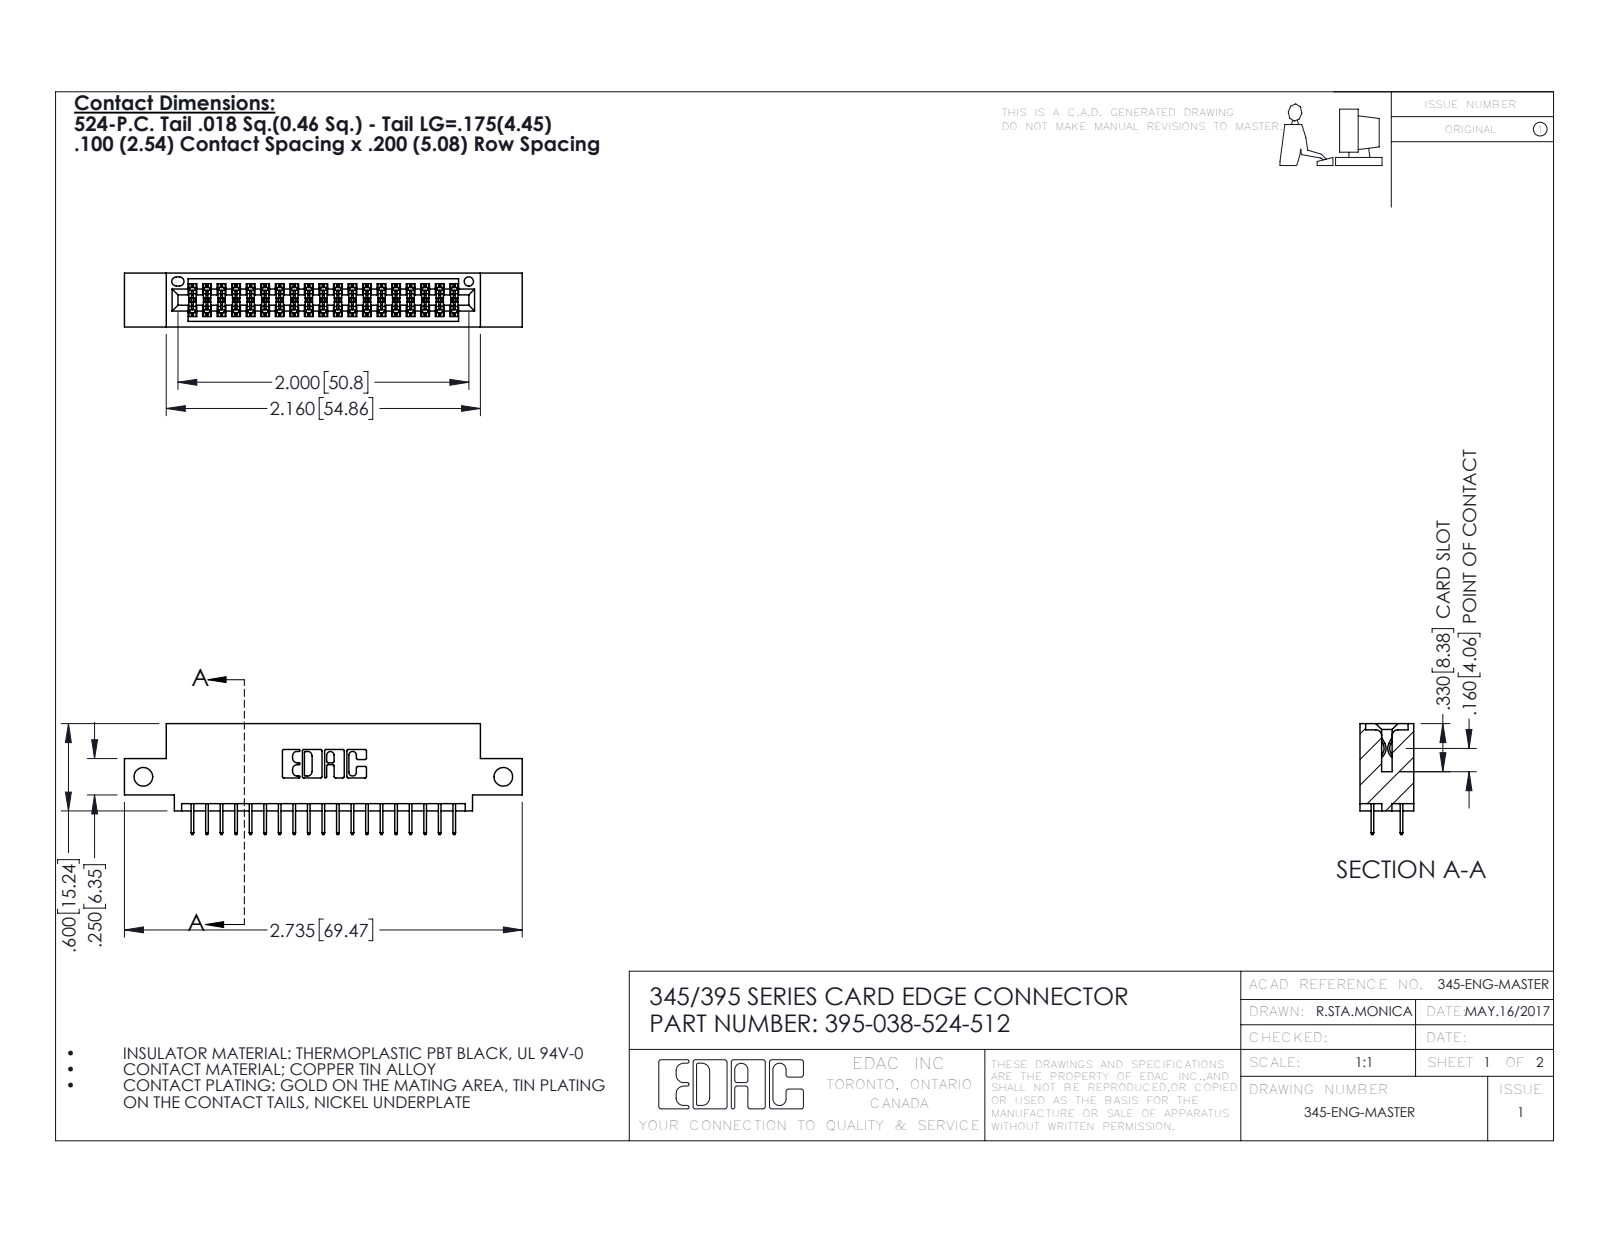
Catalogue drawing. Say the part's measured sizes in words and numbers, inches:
The part is named "395-038-524-512; 345 Part_0.110 Offset - Side Mount; 345-292-001_345-293-124". Its 3-D file was written by "SolidWorks 2016 (CONFIG_CONTROL_DESIGN)". It is 39 solids with 2182 faces: 1566 planar, 616 cylindrical and 0 other. Overall it measures 2.735 by 0.762 by 0.37 inches. Its volume is 0.385 cubic inches and its surface area 13.48 square inches. Round holes: 2 of diameter 0.128, 1 of diameter 0.064. Partial cylindrical surfaces (rounded edges, fillets, slot ends): 57 of radius 0.006, 22 of radius 0.01, 6 of radius 0.007, 6 of radius 0.031, 3 of radius 0.026, 2 of radius 0.014, 2 of radius 0.019, 2 of radius 0.022. The main face-to-face distances are 0.072, 0.298, 0.2, 0.37, 0.098, 0.272, 0.025, 0.225, 0.072, 0.175. The hole center spacings are 2.475.
